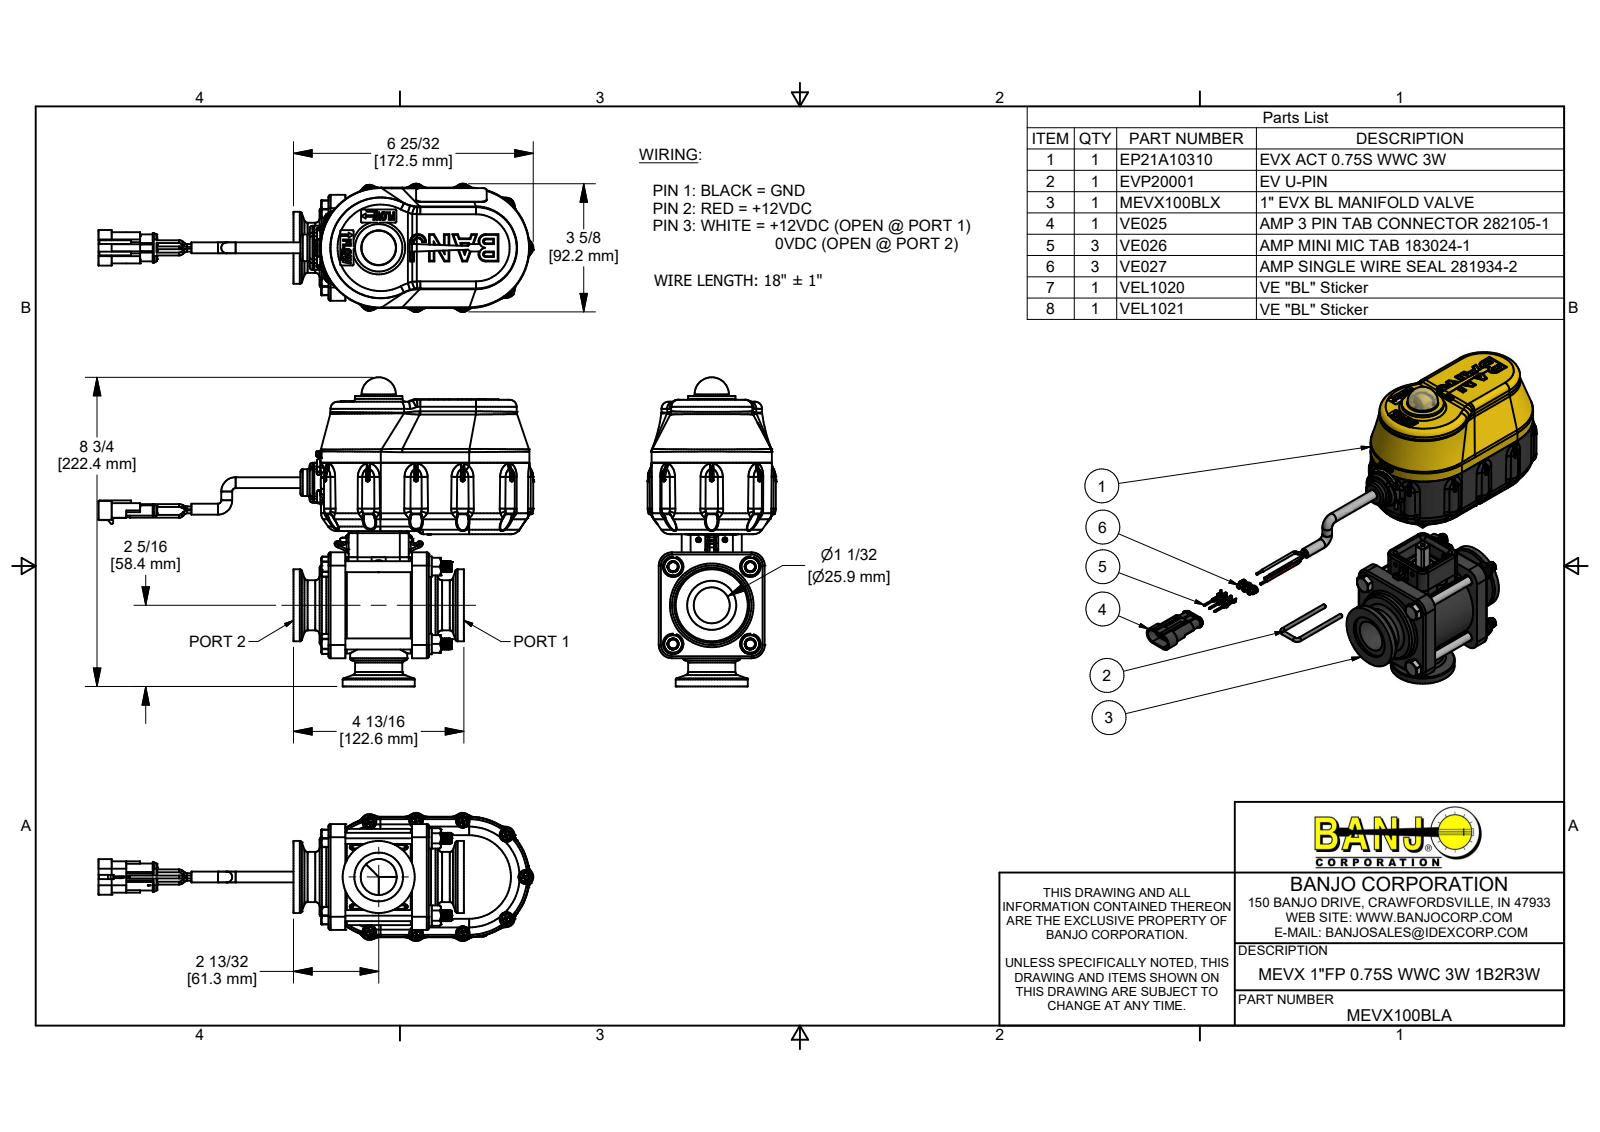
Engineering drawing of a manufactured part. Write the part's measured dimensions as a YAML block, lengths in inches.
part_name: "MEVX100BLA; MEVX100BLX; MEVX10354AB; MEVX10354ABX (+8 more)"
step_written_by: "Autodesk Inventor 2021 (AUTOMOTIVE_DESIGN)"
units: inches
bodies: {solids: 105, faces: 12721, planar: 3548, cylindrical: 3707, other: 5466}
overall_size: [12.32, 8.757, 3.63]
volume: 53.93
surface_area: 610.9
round_holes:
  - {diameter: 0.095, count: 11}
  - {diameter: 0.15, count: 11}
  - {diameter: 0.08, count: 7}
  - {diameter: 0.107, count: 4}
  - {diameter: 0.126, count: 4}
  - {diameter: 0.135, count: 4}
  - {diameter: 0.136, count: 4}
  - {diameter: 0.148, count: 4}
  - {diameter: 0.15, count: 4}
  - {diameter: 0.17, count: 4}
  - {diameter: 0.252, count: 4}
  - {diameter: 0.322, count: 4}
round_bosses_or_shafts:
  - {diameter: 0.268, count: 60}
  - {diameter: 0.25, count: 17}
  - {diameter: 0.08, count: 15}
  - {diameter: 0.14, count: 11}
  - {diameter: 0.108, count: 11}
  - {diameter: 0.085, count: 11}
  - {diameter: 0.058, count: 6}
  - {diameter: 0.313, count: 5}
partial_cylinders:
  - {radius: 0.013, count: 180}
  - {radius: 0.04, count: 145}
  - {radius: 0.01, count: 94}
  - {radius: 0.02, count: 94}
  - {radius: 0.005, count: 57}
  - {radius: 0.03, count: 47}
  - {radius: 0.06, count: 42}
  - {radius: 0.015, count: 33}
face_to_face_distances: [0.1, 2.565, 0.48, 0.055, 0.211, 0.06, 0.151, 2.365, 0.125, 1.896]
hole_center_spacings: [0.843, 0.913, 1.032, 1.547, 1.662, 1.891, 2.188, 2.656]
